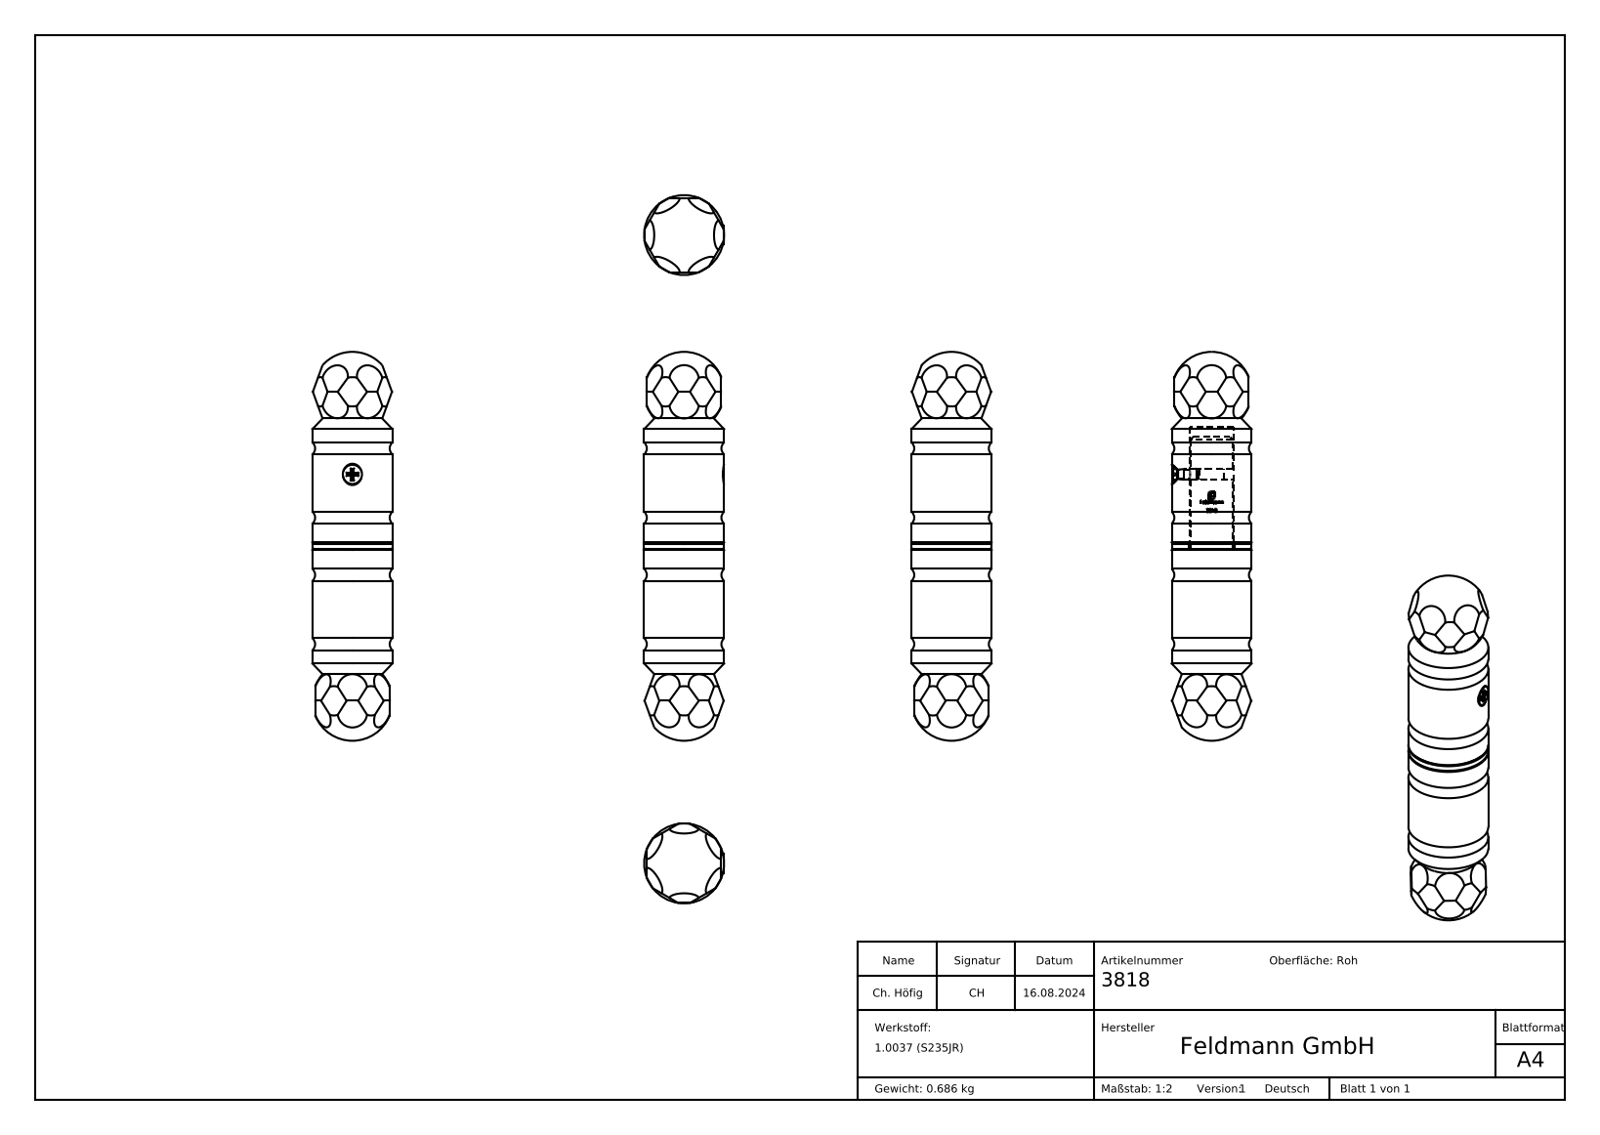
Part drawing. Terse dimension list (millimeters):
name: DIN 965_DIN 965 M4x10; 3817 und 3818 Teil1-3_3818 Teil1; 3817 und 3818 Teil1-3_3818 Teil3; 3818 (+1 more)
written by: SolidWorks 2018 (CONFIG_CONTROL_DESIGN)
unit: mm
bodies: 4 solids, 338 faces (144 planar, 36 cylindrical, 158 other)
size: 146 × 30 × 30
volume: 87 809 mm³; area: 21 136 mm²
holes: 1× ⌀3.3, 1× ⌀16.5, 1× ⌀17
bosses: 1× ⌀30, 1× ⌀16, 1× ⌀9, 1× ⌀7.2, 1× ⌀4, 1× ⌀3.6
rounds: 1× R8.35
face distances: 27.91, 2, 27.9, 46, 44, 42, 40, 4, 16.1, 30.1
